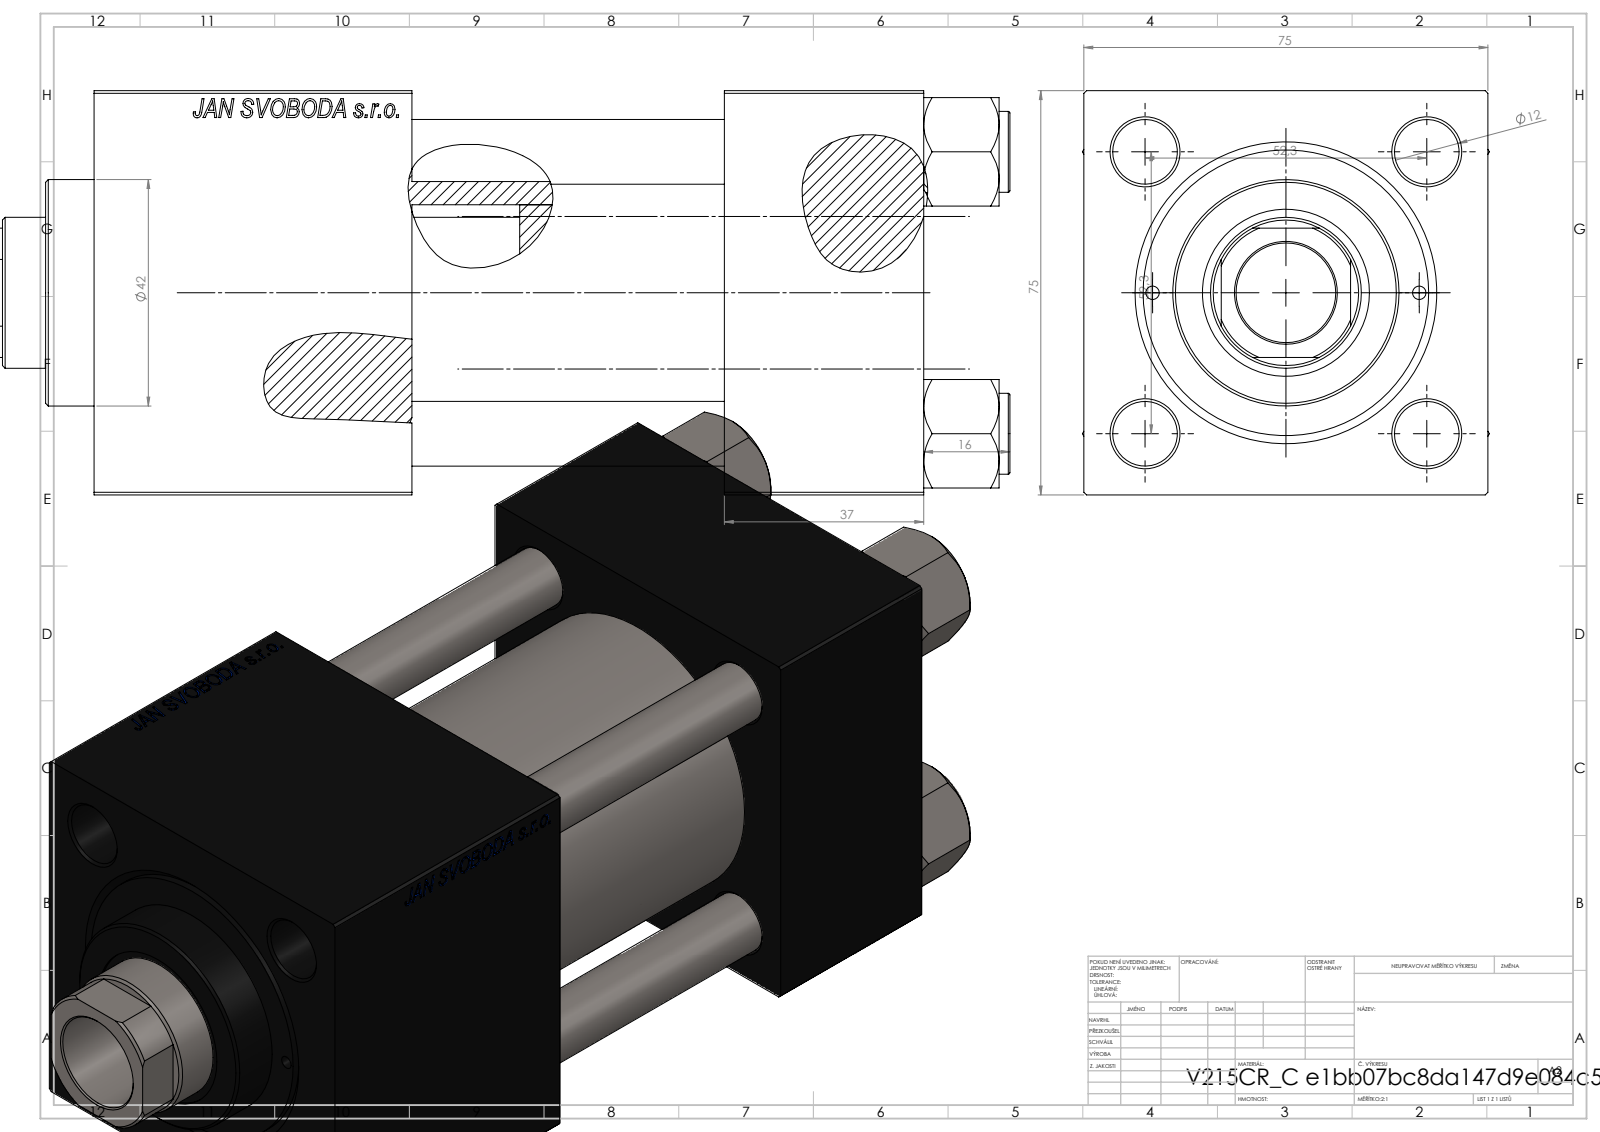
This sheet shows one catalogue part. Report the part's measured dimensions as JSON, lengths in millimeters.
{"part_name": "V215_VC_A; NUT_M5_C; V215CR_VCP_C; V215CR_C_TYCINKA (+1 more)", "step_written_by": "SolidWorks 2019 (CONFIG_CONTROL_DESIGN)", "units": "millimeters", "bodies": {"solids": 11, "faces": 1155, "planar": 528, "cylindrical": 91, "other": 536}, "overall_size": [195, 75.54, 75], "volume_mm3": 668945, "surface_area_mm2": 151012, "round_holes": [[12, 4], [2.5, 2], [7, 2], [20.96, 2], [30, 2], [18.5, 1], [28, 1], [31, 1], [41, 1], [50, 1], [53, 1]], "round_bosses_or_shafts": [[15, 4], [56, 1], [42, 1]], "partial_cylinders_radius": [[13.5, 1]], "face_to_face_distances": [75, 37, 154, 117, 95, 58, 59, 125.3, 88.3, 30.3], "hole_center_spacings": [26.19, 36.98, 52.3, 57.22, 24.75, 73.96, 49.5, 93.5]}
